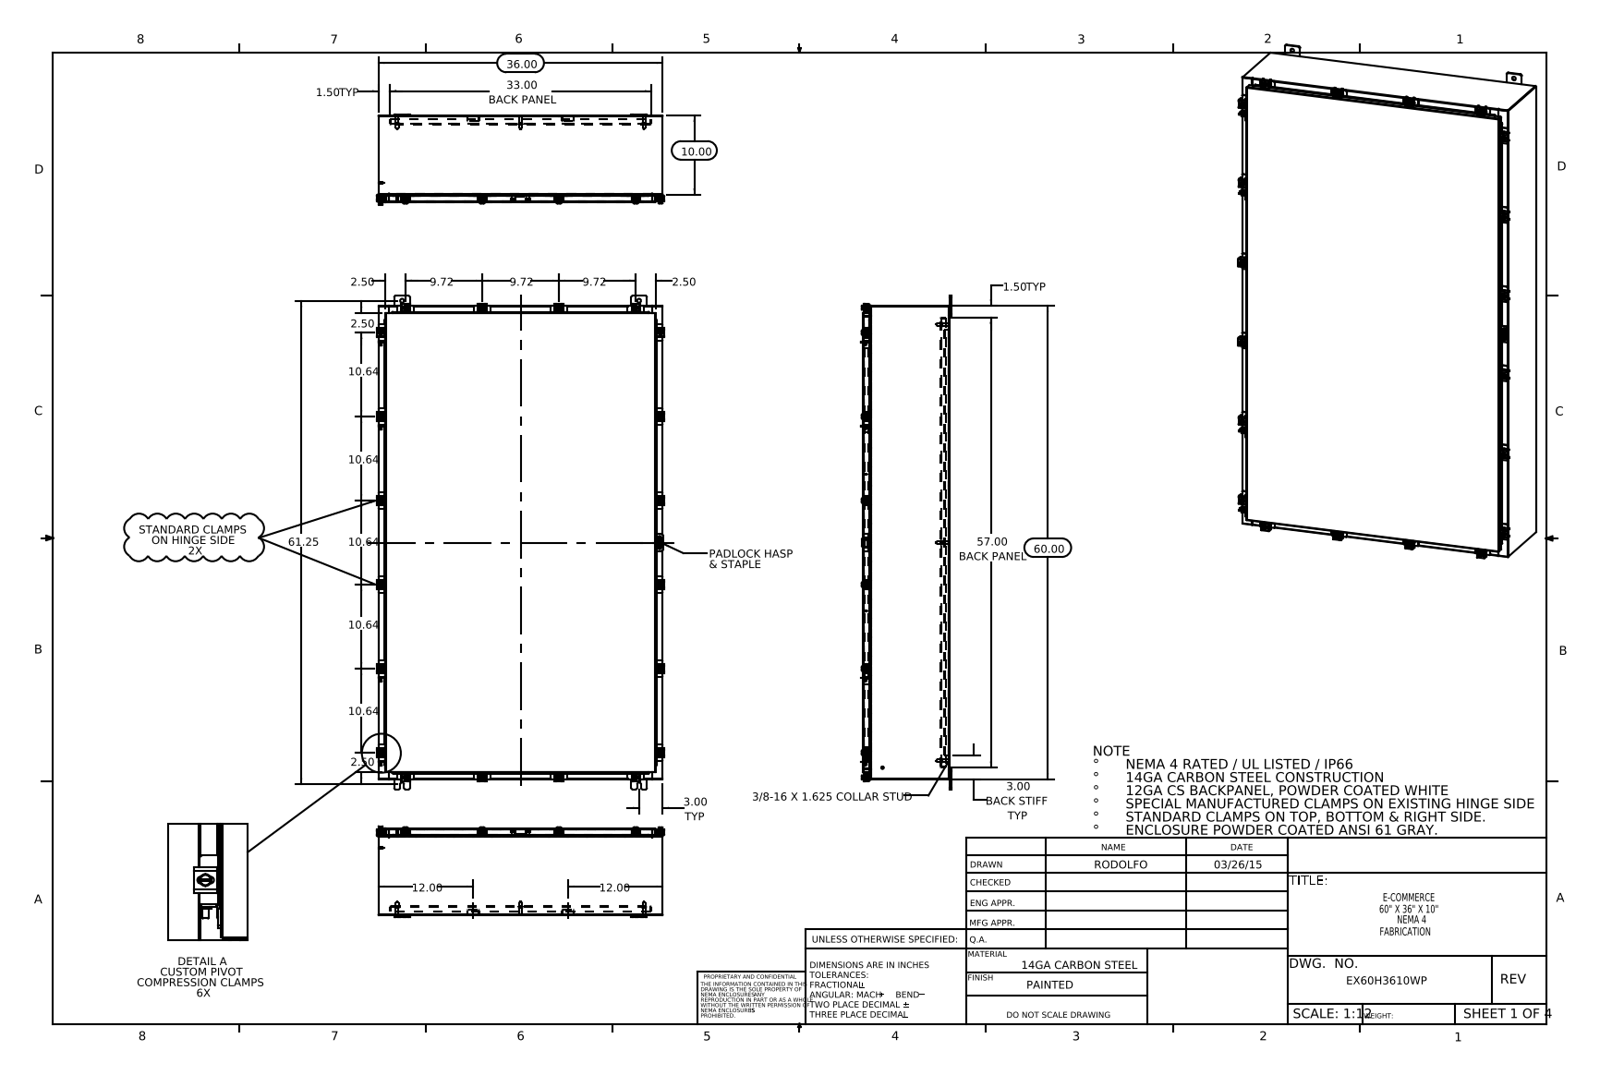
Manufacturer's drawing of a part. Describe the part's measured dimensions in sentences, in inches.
The part is named "30X10 Clamp Bracket2; HW-CLN-NH-20320; EX60H3610WP Bottom; 22101002_RTP29 (+8 more)". Its 3-D file was written by "SolidWorks 2014 (CONFIG_CONTROL_DESIGN)". It is 140 solids with 3424 faces: 1773 planar, 1319 cylindrical and 332 other. Overall it measures 62.5 by 36.421 by 11.453 inches. Its volume is 764.2 cubic inches and its surface area 18 917 square inches. Round holes: 20 of diameter 0.213, 20 of diameter 0.26, 12 of diameter 0.5, 9 of diameter 0.25, 1 of diameter 0.125. Round bosses or shafts: 20 of diameter 0.5, 20 of diameter 0.25, 16 of diameter 0.399, 8 of diameter 0.625, 8 of diameter 0.375, 8 of diameter 0.33, 8 of diameter 0.157, 8 of diameter 0.14. Partial cylindrical surfaces (rounded edges, fillets, slot ends): 84 of radius 0.06, 40 of radius 0.141, 38 of radius 0.013, 36 of radius 0.12, 34 of radius 0.088, 32 of radius 0.09, 29 of radius 0.05, 28 of radius 0.145. The main face-to-face distances are 0.075, 10.9, 10.826, 0.104, 10.975, 1, 1.075, 9.826, 9.9, 1.179. The hole center spacings are 1.969, 2.224, 2.347, 13.972, 14.729, 16.126, 27.625, 29.744.
